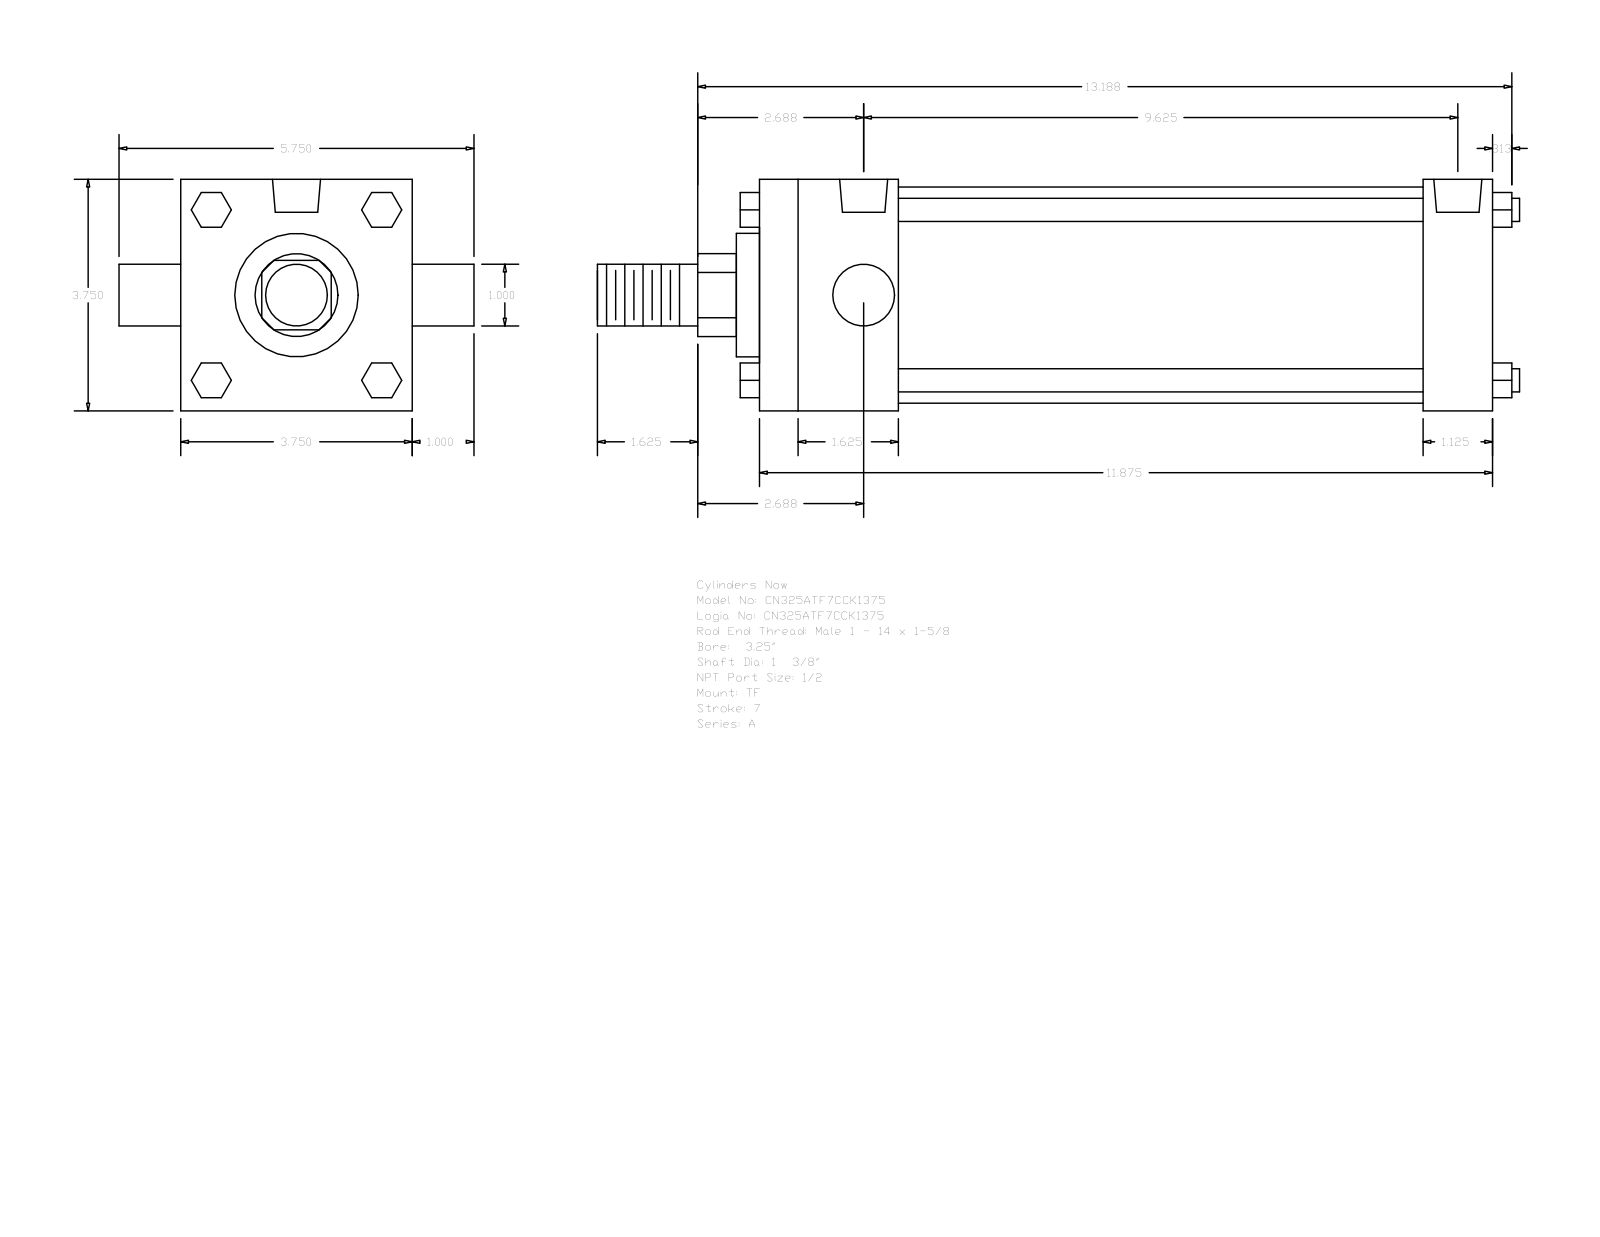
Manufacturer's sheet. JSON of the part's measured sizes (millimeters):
{"part_name": "A_TF__0325_1.375", "step_written_by": "GSSL Pune (CONFIG_CONTROL_DESIGN)", "units": "millimeters", "bodies": {"solids": 0, "faces": 120, "planar": 92, "cylindrical": 28, "other": 0}, "overall_size": [379.41, 146.05, 95.25], "round_holes": [[8.73, 3], [19.77, 2]], "round_bosses_or_shafts": [[9.53, 4], [25.4, 2], [88.9, 1], [50.8, 1], [34.92, 1]], "partial_cylinders_radius": [[17.06, 1]], "face_to_face_distances": [95.24, 301.62, 57.15, 273.05, 215.9, 244.47, 28.57, 66.67, 9.52, 282.57], "hole_center_spacings": [3.18, 241.3, 238.12, 244.48]}
